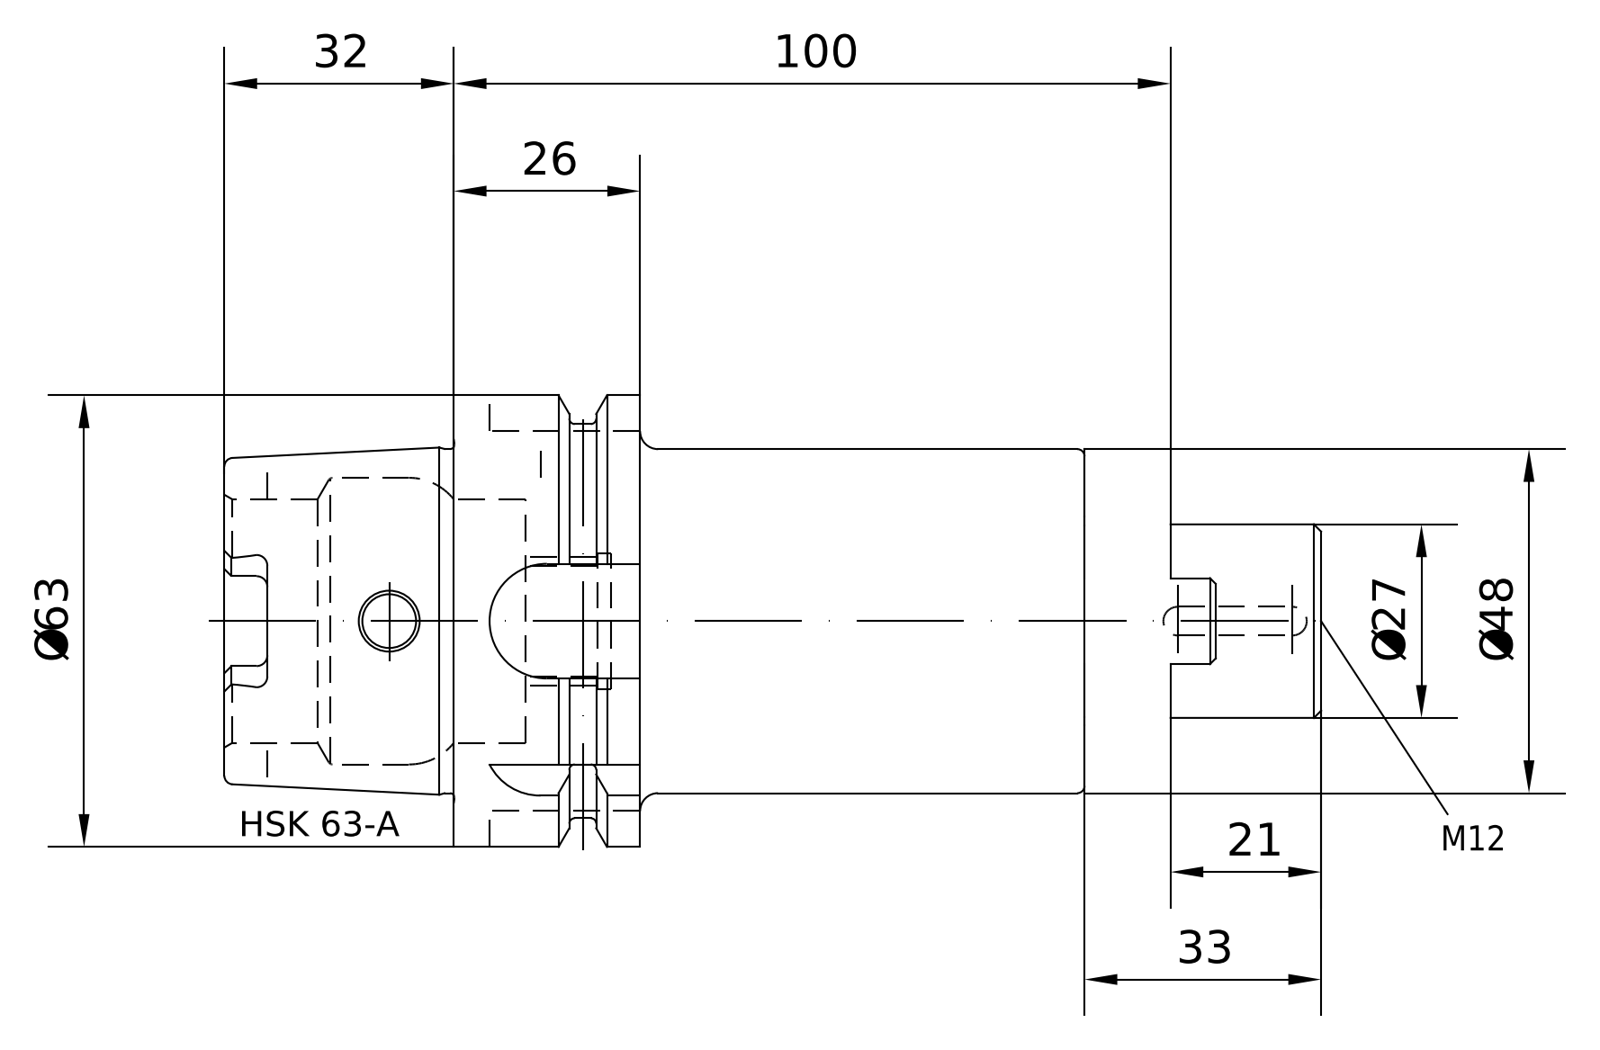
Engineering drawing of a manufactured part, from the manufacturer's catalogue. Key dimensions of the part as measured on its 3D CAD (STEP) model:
Part name (STEP PRODUCT): A63-041-27; 85-200-27; A63-041-27_ASM
STEP written by: PRO/ENGINEER BY PARAMETRIC TECHNOLOGY CORPORATION, 2010430 (CONFIG_CONTROL_DESIGN)
Units: millimetres
Bodies: 2 solids, 266 faces (124 planar, 64 cylindrical, 78 other)
Overall size (bounding box): 153 × 63 × 63
Volume: 221 578 mm³ · Surface area: 44 003 mm²
Round holes (diameter × count): ⌀7.5 ×1, ⌀10 ×1, ⌀10.2 ×1, ⌀12 ×1, ⌀16.92 ×1, ⌀18.32 ×1, ⌀18.66 ×1, ⌀27.36 ×1, ⌀31.5 ×1, ⌀34 ×1, ⌀40 ×1
Round bosses / shafts (diameter × count): ⌀63 ×1, ⌀55 ×1, ⌀48.04 ×1, ⌀48 ×1, ⌀27 ×1, ⌀18 ×1
Partial cylindrical surfaces — rounded edges, fillets, slot ends (radius × count): R1.5 ×6, R3 ×4, R3.5 ×2, R6.05 ×1, R8 ×1, R8.02 ×1, R9.02 ×1
Main face-to-face distances: 88, 26, 10, 62, 100, 74, 12, 121, 32, 16
